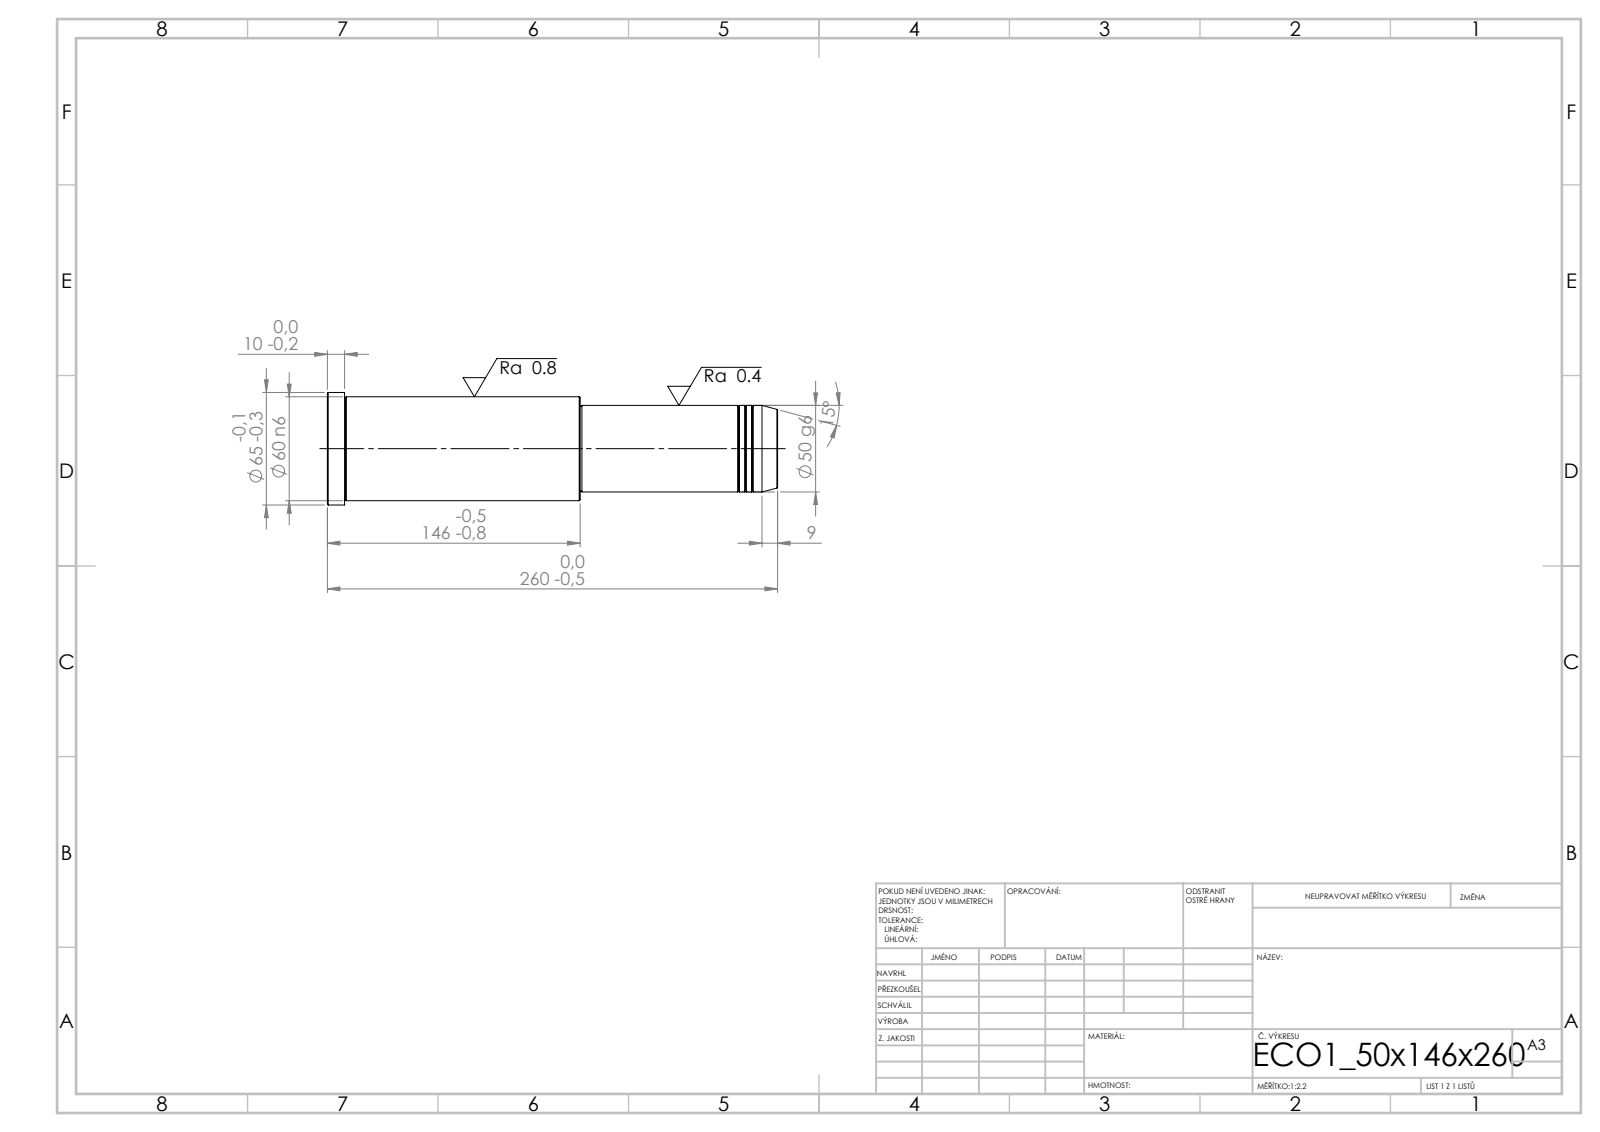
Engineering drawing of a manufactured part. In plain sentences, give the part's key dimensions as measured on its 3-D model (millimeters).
Its 3-D file was written by "SolidWorks 2019 (CONFIG_CONTROL_DESIGN)". It is 1 solid with 43 faces: 5 planar, 14 cylindrical and 24 other. Overall it measures 260 by 65 by 65 millimeters. Its volume is 639 515 cubic millimeters and its surface area 52 224 square millimeters. Round bosses or shafts: 1 of diameter 65, 1 of diameter 60, 1 of diameter 50, 1 of diameter 49. The main face-to-face distances are 260, 114, 146, 250, 136, 10, 113, 1, 137, 147.
